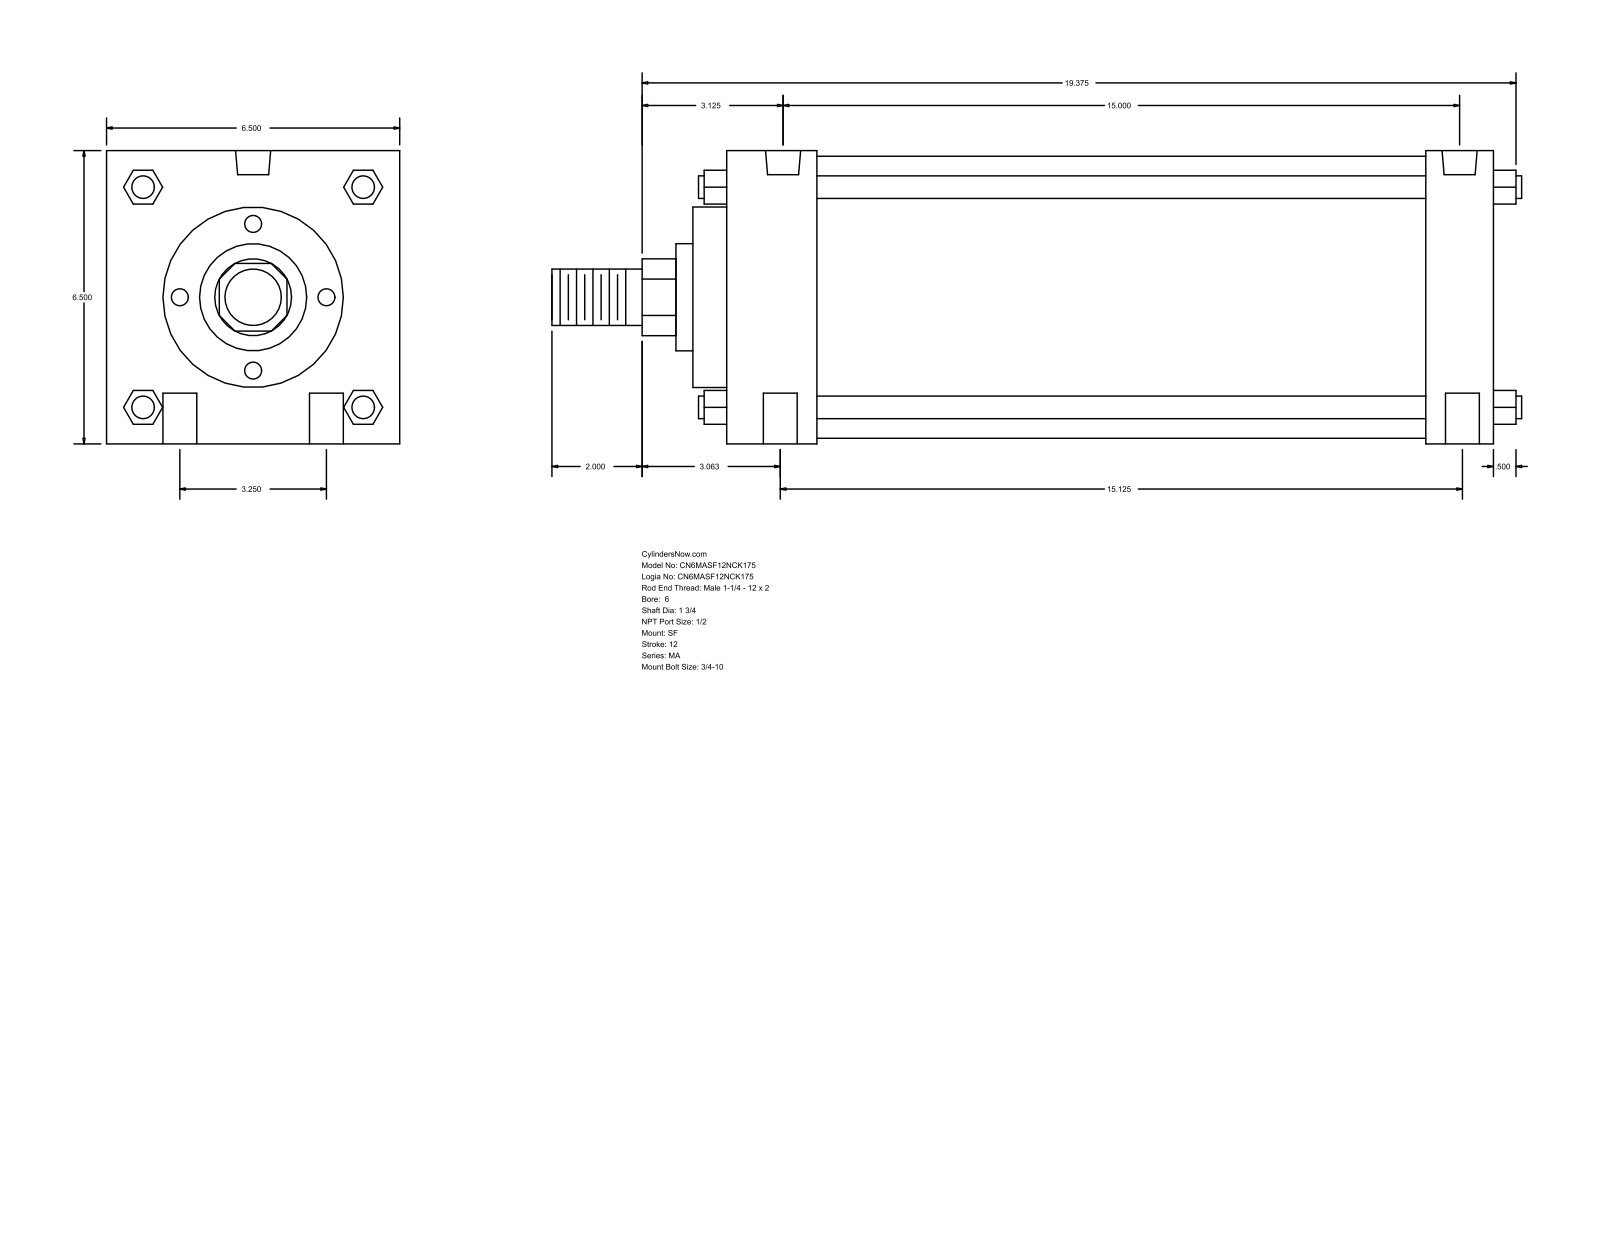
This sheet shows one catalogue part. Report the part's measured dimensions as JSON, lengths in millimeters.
{"part_name": "MA_SF__0600_1.75", "step_written_by": "GSSL Pune (CONFIG_CONTROL_DESIGN)", "units": "millimeters", "bodies": {"solids": 0, "faces": 126, "planar": 95, "cylindrical": 31, "other": 0}, "overall_size": [546.1, 165.1, 165.1], "round_holes": [[19.05, 4], [17.46, 2], [19.77, 2]], "round_bosses_or_shafts": [[12.7, 4], [158.75, 1], [101.6, 1], [60.33, 1], [44.45, 1], [31.75, 1]], "partial_cylinders_radius": [[21.63, 1]], "face_to_face_distances": [165.1, 431.81, 19.05, 50.8, 393.7, 38.11, 342.9, 381.01, 69.85, 412.75], "hole_center_spacings": [41.3, 82.54, 381, 384.17, 384.8, 384.81, 392.94]}
